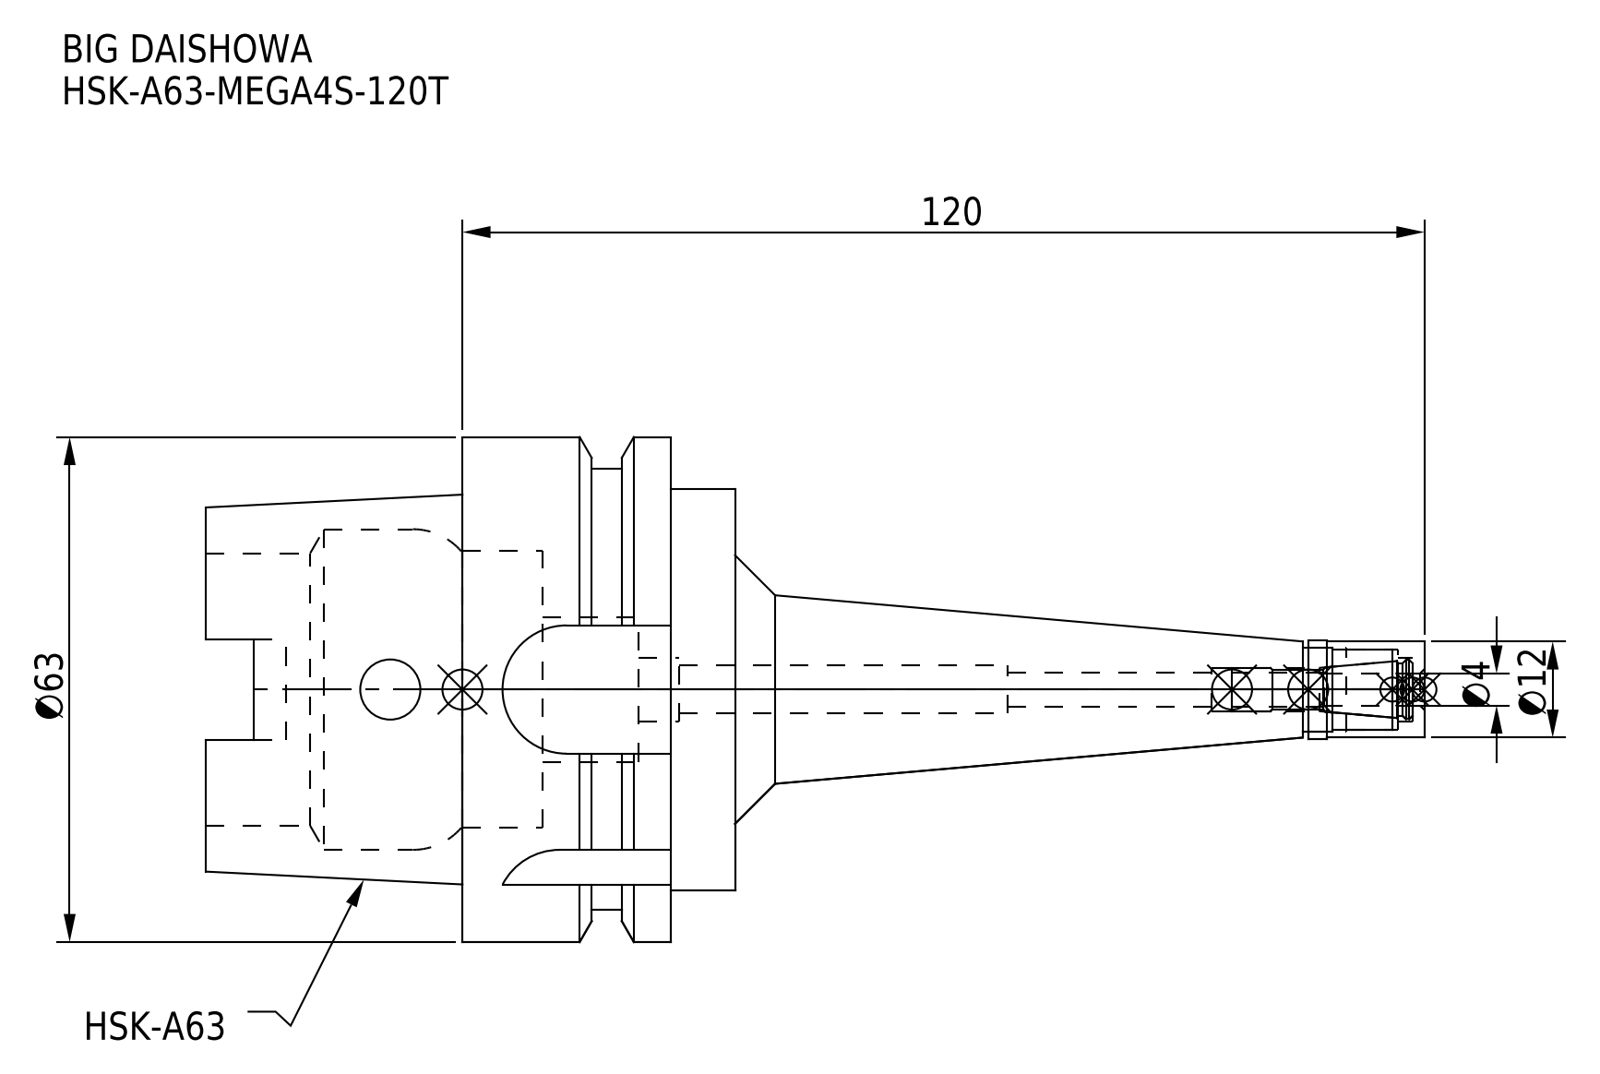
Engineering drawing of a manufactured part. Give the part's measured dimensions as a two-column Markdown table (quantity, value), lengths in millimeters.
| quantity | value |
| --- | --- |
| part name | HSK-A63-MEGA4S-120T-040-FreeParts; MGN4S_1.stp; HSK-A63-MEGA4S-120T-040.stp; DXF_TEMP_ASSY_ASM_4_ASM.stp (+3 more) |
| STEP written by | SolidWorks 2019 (CONFIG_CONTROL_DESIGN) |
| units | millimeters |
| bodies | 2 solids, 125 faces (48 planar, 55 cylindrical, 22 other) |
| overall size | 152 × 63 × 63 |
| volume | 116 844 mm³ |
| surface area | 30 261 mm² |
| round holes (diameter × count) | 4.1 × 1, 4.2 × 1, 5.4 × 1, 6 × 1, 7.5 × 1, 8 × 1, 10 × 1, 10.5 × 1, 18 × 1, 34 × 1, 34.5 × 1, 40 × 1 |
| round bosses / shafts (diameter × count) | 63 × 1, 55 × 1, 50 × 1, 12.3 × 1, 12 × 1 |
| partial cylindrical surfaces (radius × count) | 2.88 × 4, 8 × 4 |
| main face-to-face distances | 34, 26, 8, 24.05, 16.05, 9.95, 66, 58, 41.95, 32 |
